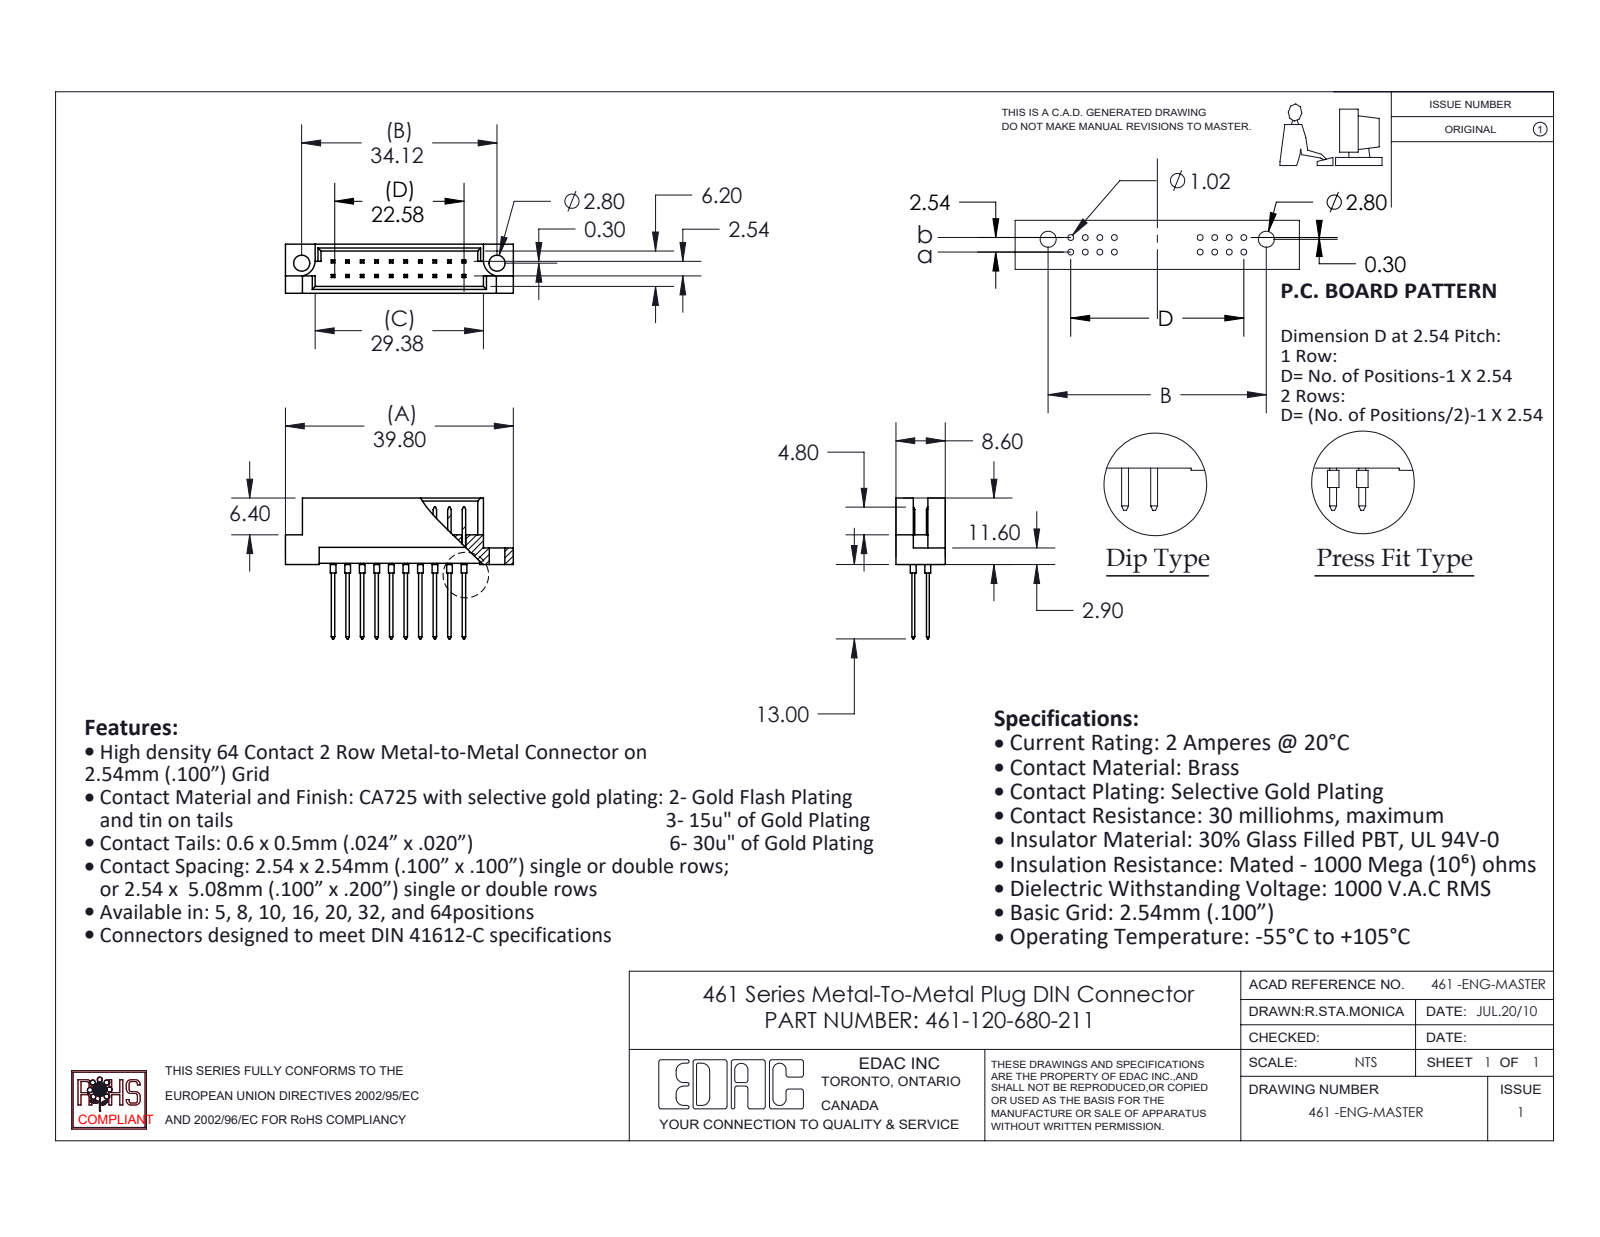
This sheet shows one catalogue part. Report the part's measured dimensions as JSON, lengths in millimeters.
{"part_name": "461-290_80; 461 Part_20; 461-120-680-211", "step_written_by": "SolidWorks 2020 (CONFIG_CONTROL_DESIGN)", "units": "millimeters", "bodies": {"solids": 21, "faces": 568, "planar": 522, "cylindrical": 46, "other": 0}, "overall_size": [39.8, 24.6, 8.6], "volume_mm3": 2055, "surface_area_mm2": 3389, "round_holes": [[2.8, 2]], "round_bosses_or_shafts": [[1, 20]], "partial_cylinders_radius": [[2.8, 2]], "face_to_face_distances": [2.54, 1.2, 7.4, 8.6, 2.78, 3.28, 5.32, 5.82, 1.58, 2.08], "hole_center_spacings": [34.12]}
